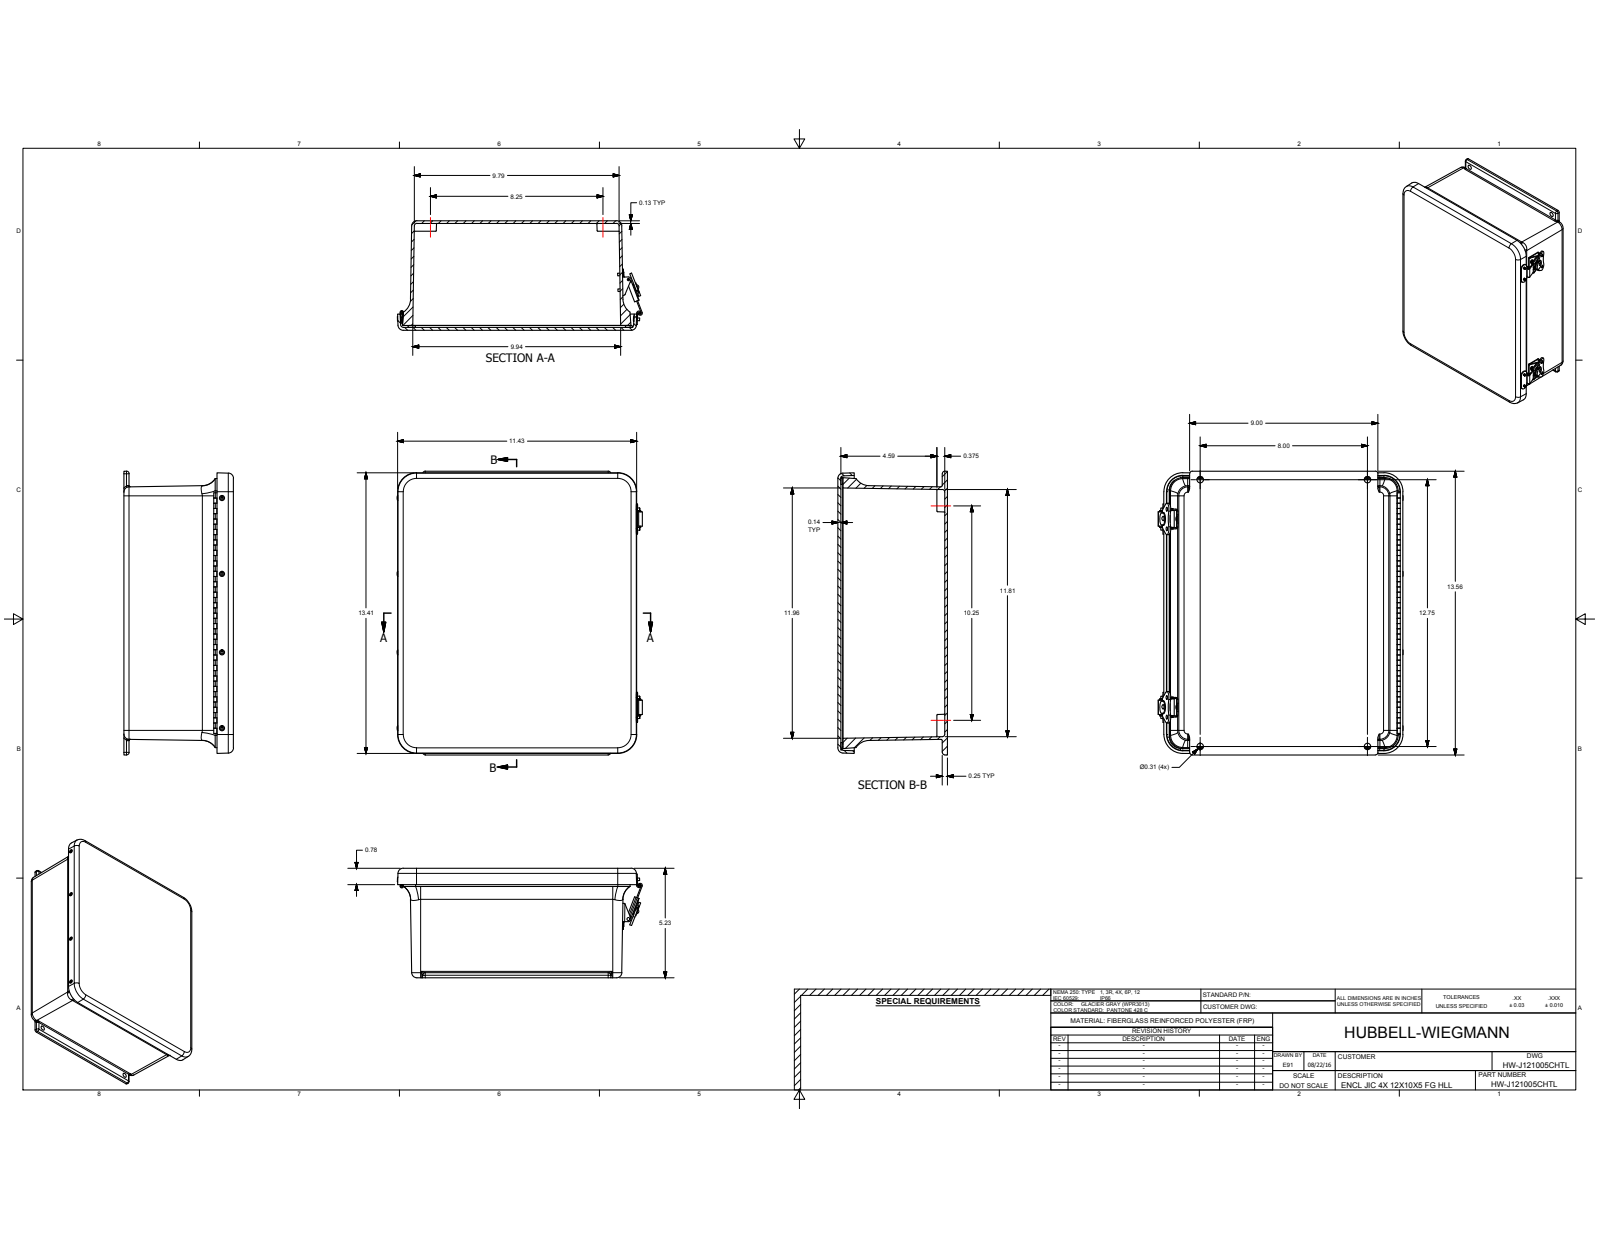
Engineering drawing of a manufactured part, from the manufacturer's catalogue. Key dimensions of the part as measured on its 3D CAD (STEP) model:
Part name (STEP PRODUCT): HW-J1210CHTL; WP1210H&LBOX; WP1210HLU; WP1210H&LCVR (+8 more)
STEP written by: Autodesk Inventor 2017 (CONFIG_CONTROL_DESIGN)
Units: millimetres
Bodies: 46 solids, 1137 faces (480 planar, 469 cylindrical, 188 other)
Overall size (bounding box): 344.5 × 297.44 × 132.97
Volume: 1 411 000 mm³ · Surface area: 772 495 mm²
Round holes (diameter × count): ⌀3.56 ×18, ⌀2.64 ×16, ⌀3.33 ×8, ⌀3.86 ×8, ⌀3.3 ×4, ⌀3.38 ×4, ⌀4.04 ×4, ⌀4.75 ×4, ⌀5.54 ×4, ⌀7.92 ×4, ⌀3.43 ×2, ⌀4.8 ×2
Round bosses / shafts (diameter × count): ⌀3.17 ×16, ⌀6.86 ×4, ⌀16.76 ×2, ⌀14.78 ×2, ⌀13.34 ×2, ⌀7.26 ×2, ⌀5.41 ×2, ⌀4.57 ×2
Partial cylindrical surfaces — rounded edges, fillets, slot ends (radius × count): R0.79 ×36, R3.17 ×17, R0.38 ×16, R1.52 ×13, R6.35 ×10, R0.29 ×8, R0.51 ×8, R1.4 ×8
Main face-to-face distances: 3.63, 132.97, 129.34, 3.18, 129.79, 126.16, 5.97, 2.34, 123.82, 127
Hole centre spacings: 228.6, 18.42, 228.63, 3.17, 3.18, 3.99, 6.35, 28.4
